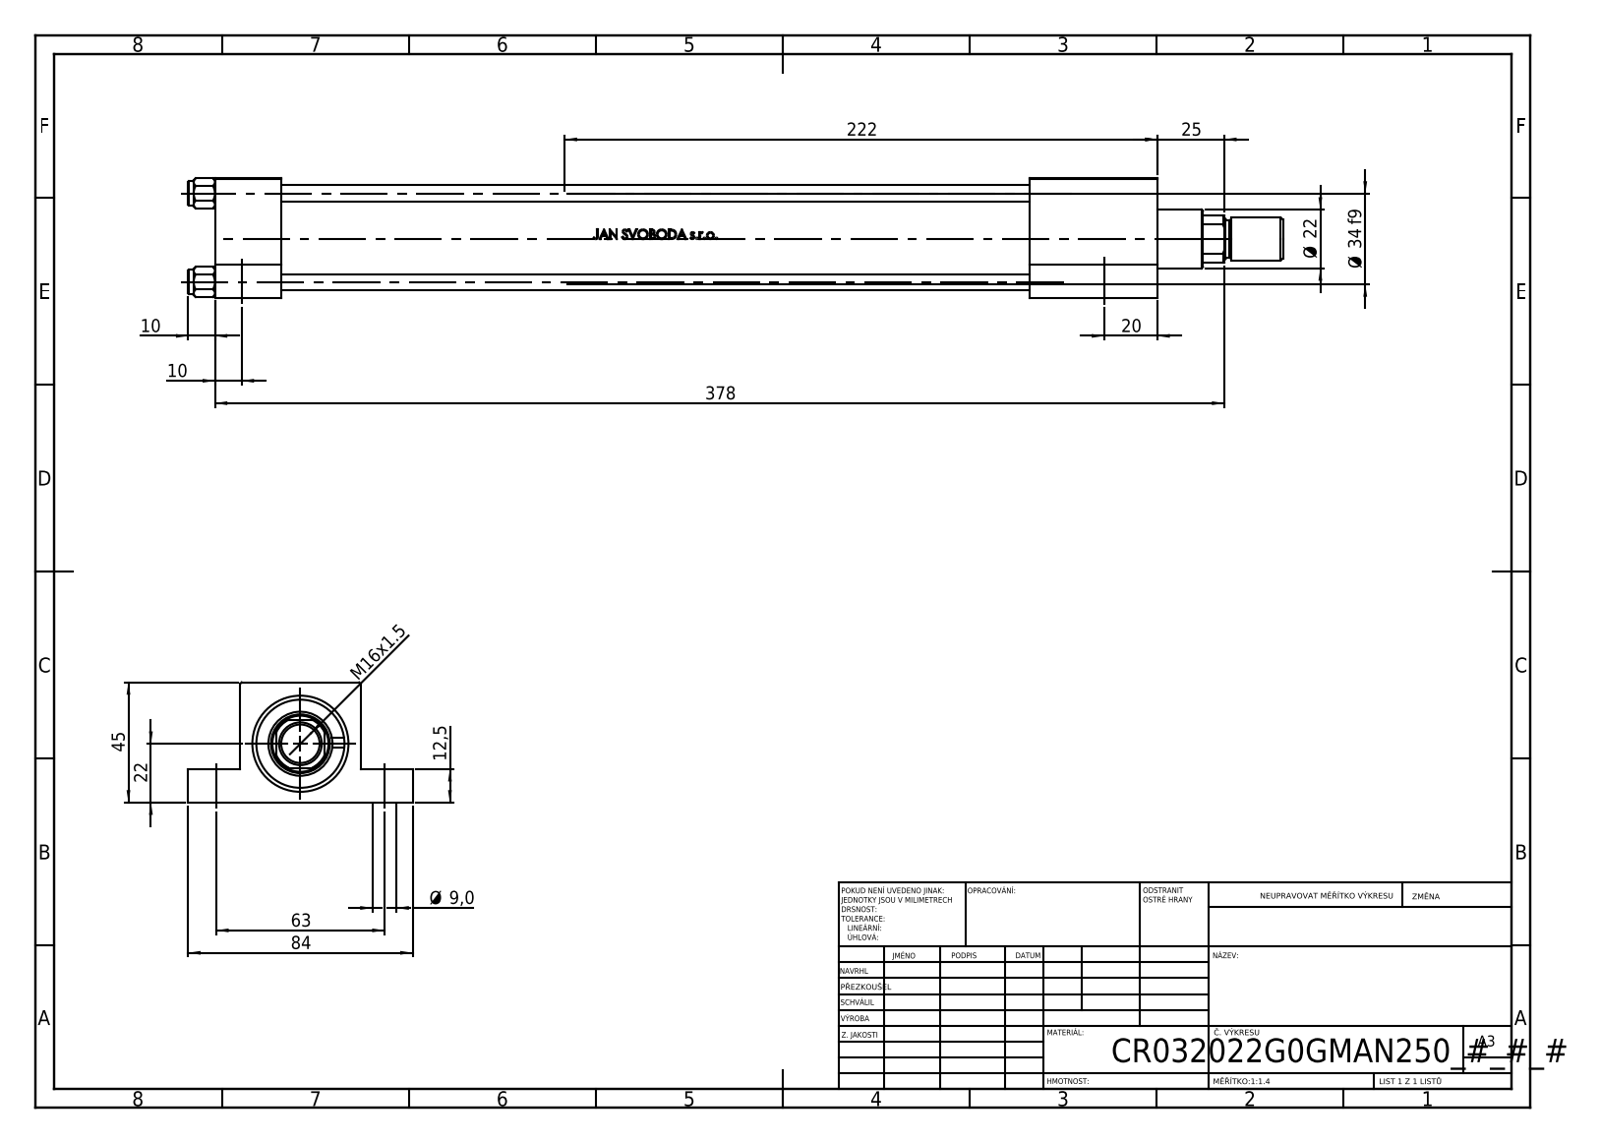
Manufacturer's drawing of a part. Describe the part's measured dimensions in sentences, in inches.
The part is named "V215_VC_A; ROD_END_AH; NUT_M5_G; V215CR_G_TYCINKA (+2 more)". Its 3-D file was written by "SolidWorks 2019 (CONFIG_CONTROL_DESIGN)". It is 12 solids with 1100 faces: 434 planar, 128 cylindrical and 538 other. Overall it measures 16.142 by 3.307 by 1.772 inches. Its volume is 26.7 cubic inches and its surface area 254.3 square inches. Round holes: 4 of diameter 0.236, 4 of diameter 0.354, 2 of diameter 0.276, 2 of diameter 0.518, 2 of diameter 0.787, 1 of diameter 0.413, 1 of diameter 0.866, 1 of diameter 0.945, 1 of diameter 0.984, 1 of diameter 1.26, 1 of diameter 1.299. Round bosses or shafts: 4 of diameter 0.354, 1 of diameter 1.496, 1 of diameter 1.339, 1 of diameter 0.63, 1 of diameter 0.551. Partial cylindrical surfaces (rounded edges, fillets, slot ends): 1 of radius 0.413. The main face-to-face distances are 1.772, 0.984, 0.492, 1.28, 13.898, 0.768, 2.539, 12.913, 12.008, 11.024. The hole center spacings are 1.307, 0.911, 0.938, 1.848, 2.48, 12.717, 12.956, 12.028.
